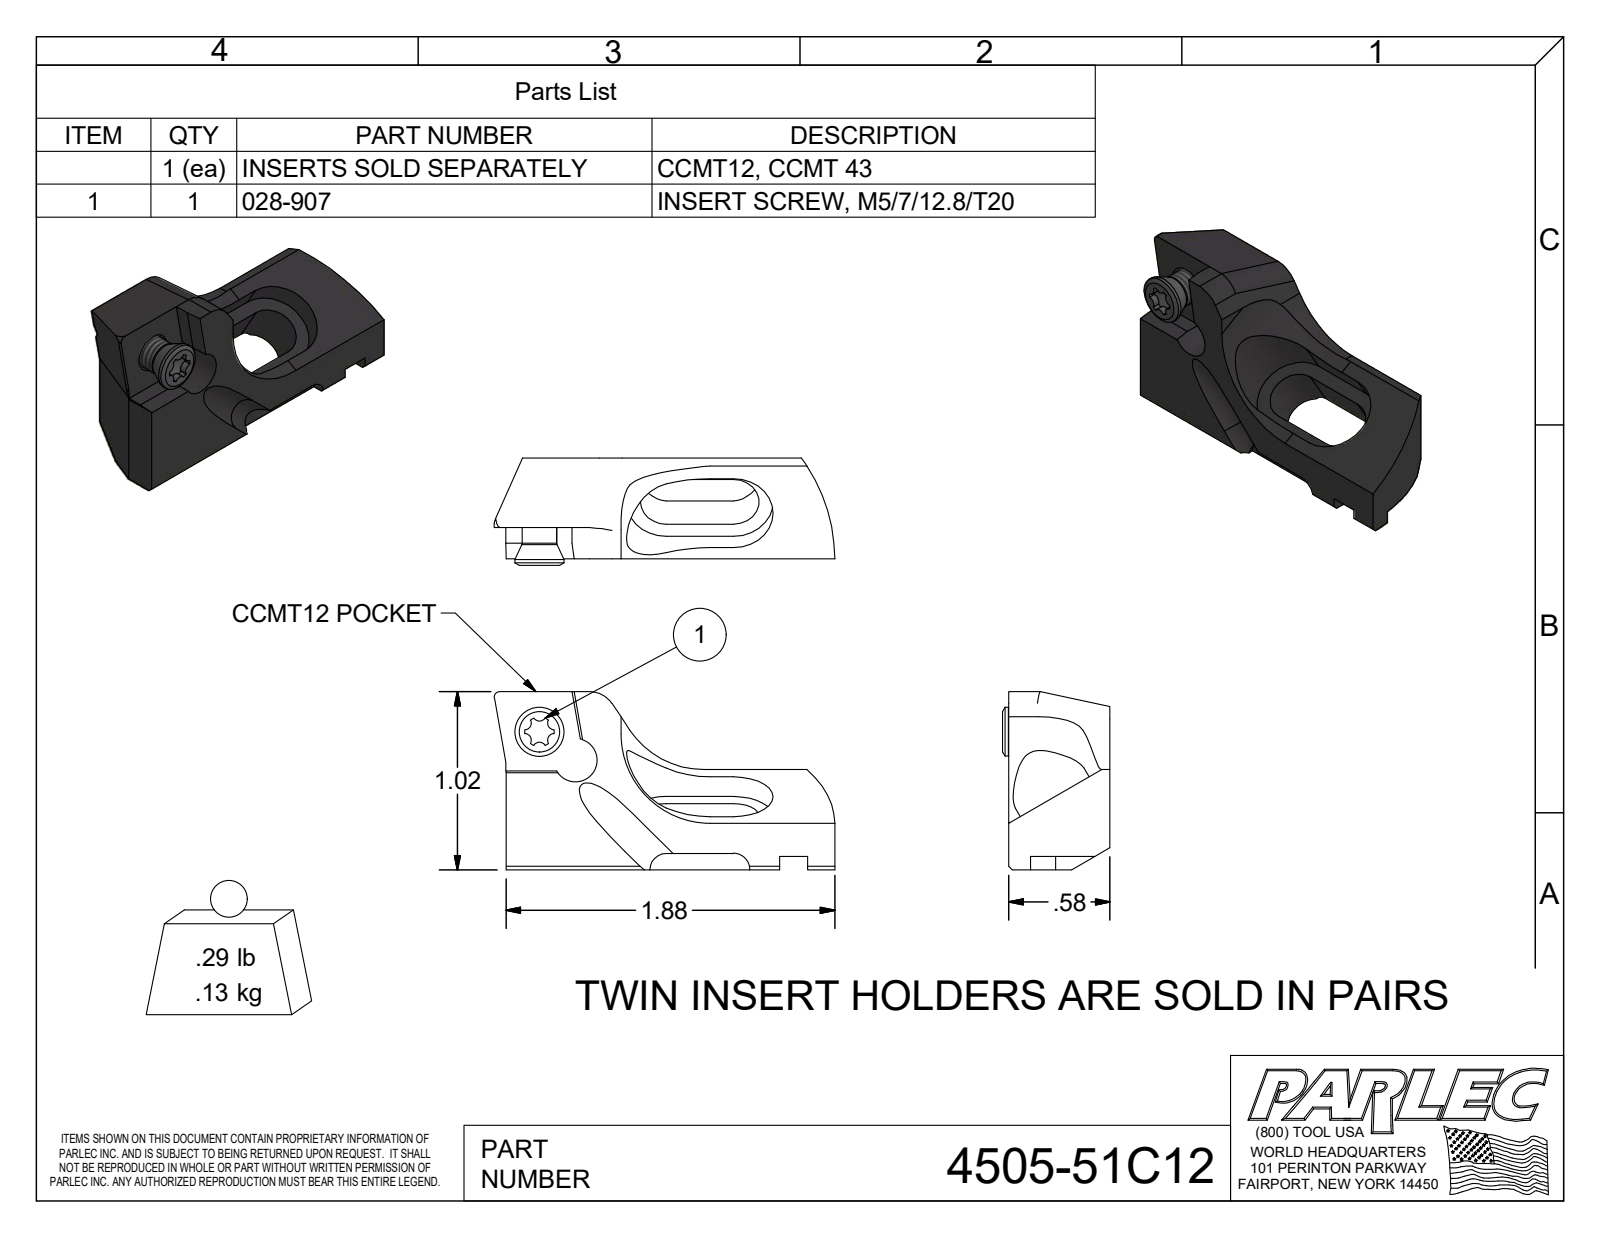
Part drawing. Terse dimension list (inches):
name: 4505-51C12 PAIR; 028-907; 814-250
written by: Autodesk Inventor 2018 (AUTOMOTIVE_DESIGN)
unit: in
bodies: 4 solids, 166 faces (92 planar, 58 cylindrical, 16 other)
size: 2.572 × 1.158 × 1.021
volume: 0.983 in³; area: 12.65 in²
holes: 2× ⌀0.163
bosses: 2× ⌀0.28, 2× ⌀0.197
rounds: 12× R0.038, 6× R0.094, 4× R0.148, 4× R0.154, 4× R0.228, 2× R0.032, 2× R0.084, 2× R0.125
face distances: 0.579, 1.158, 0.411, 0.399, 0.759, 0.18, 0.281, 0.13, 2.398, 0.08
hole spacings: 2.055
